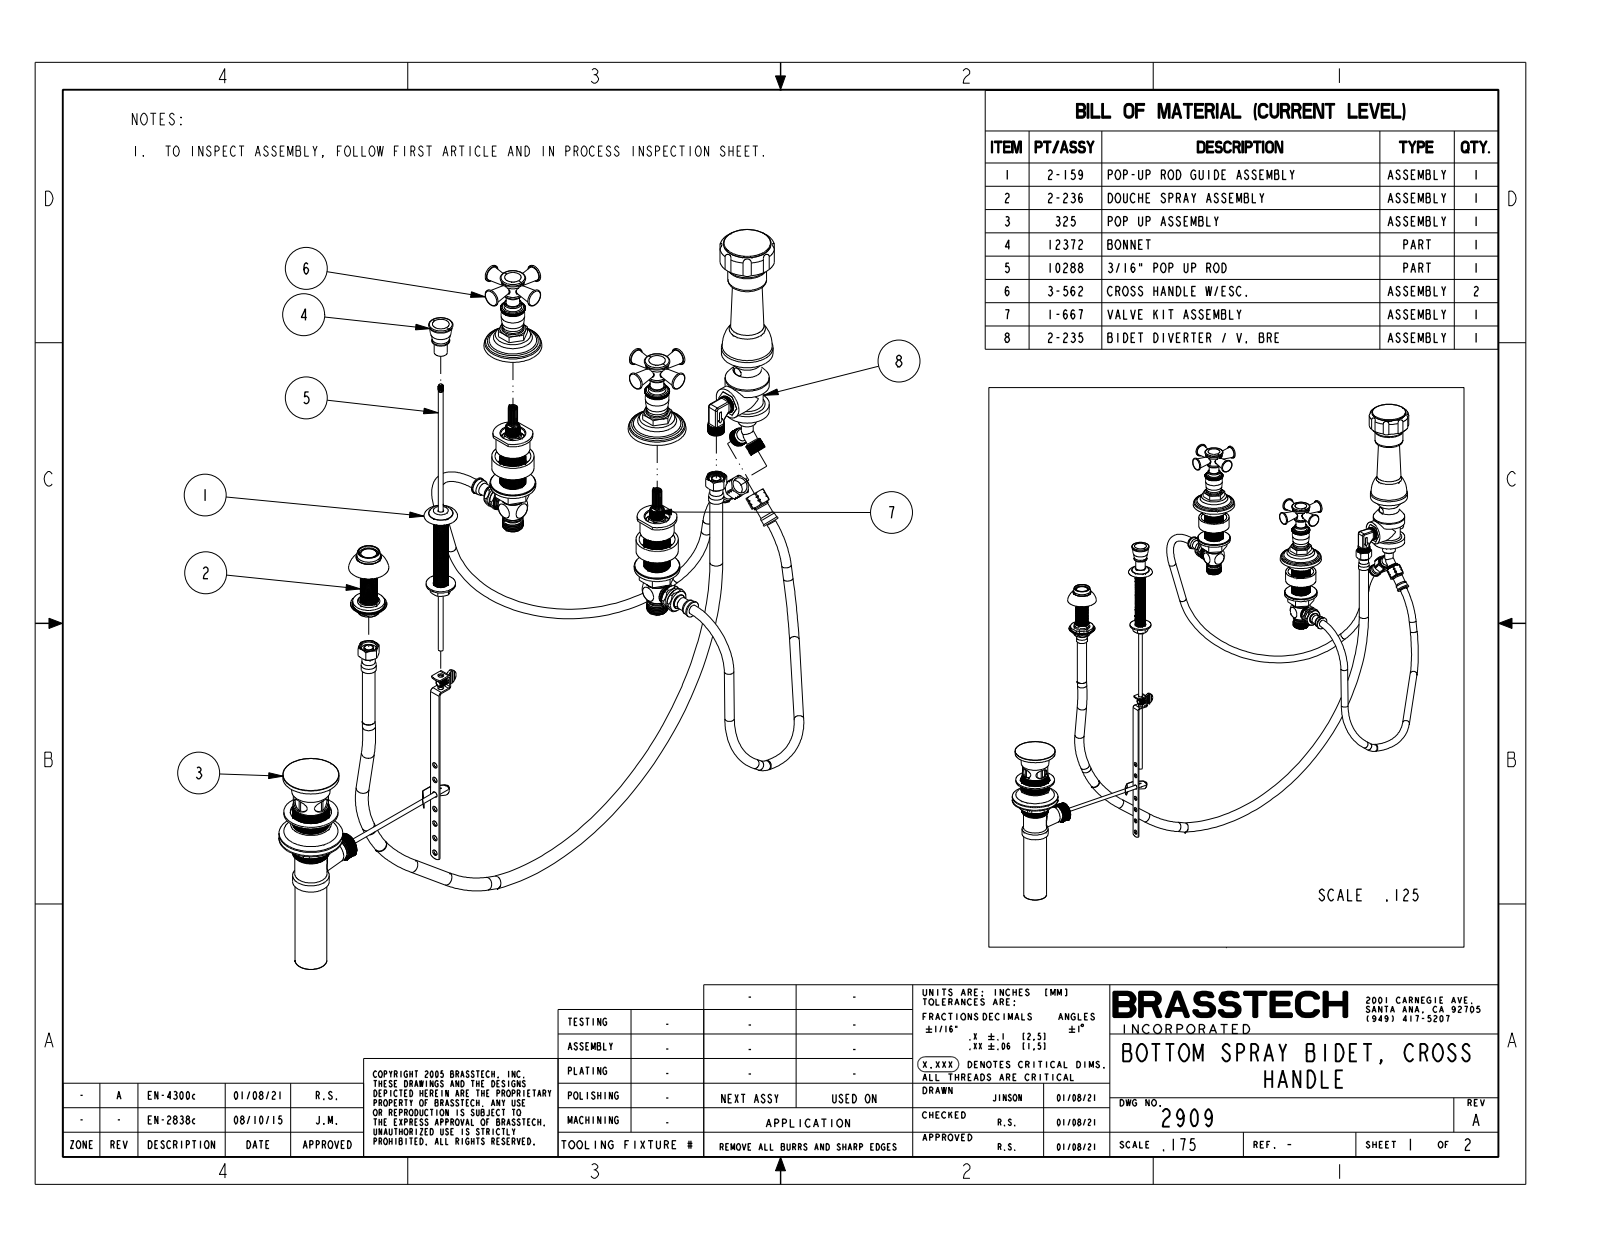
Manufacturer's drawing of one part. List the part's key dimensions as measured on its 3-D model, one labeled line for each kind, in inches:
Part name (STEP PRODUCT): 2909
STEP written by: CREO PARAMETRIC BY PTC INC, 2018400 (CONFIG_CONTROL_DESIGN)
Units: inches
Bodies: 5 solids, 920 faces (446 planar, 52 cylindrical, 422 other)
Overall size (bounding box): 22.855 × 10.45 × 5.353
Volume: 19.76 in³ · Surface area: 100 in²
Round holes (diameter × count): ⌀0.625 ×1, ⌀0.792 ×1, ⌀0.94 ×1
Round bosses / shafts (diameter × count): ⌀0.98 ×2, ⌀0.686 ×2, ⌀0.53 ×2, ⌀2.025 ×1, ⌀1.52 ×1, ⌀0.925 ×1, ⌀0.775 ×1, ⌀0.51 ×1
Partial cylindrical surfaces — rounded edges, fillets, slot ends (radius × count): R0.21 ×8, R0.357 ×1, R1.077 ×1
Main face-to-face distances: 0.534, 3.468, 2.934, 6.928, 1.025, 1.874, 1.34, 1.594, 0.803, 1.503
